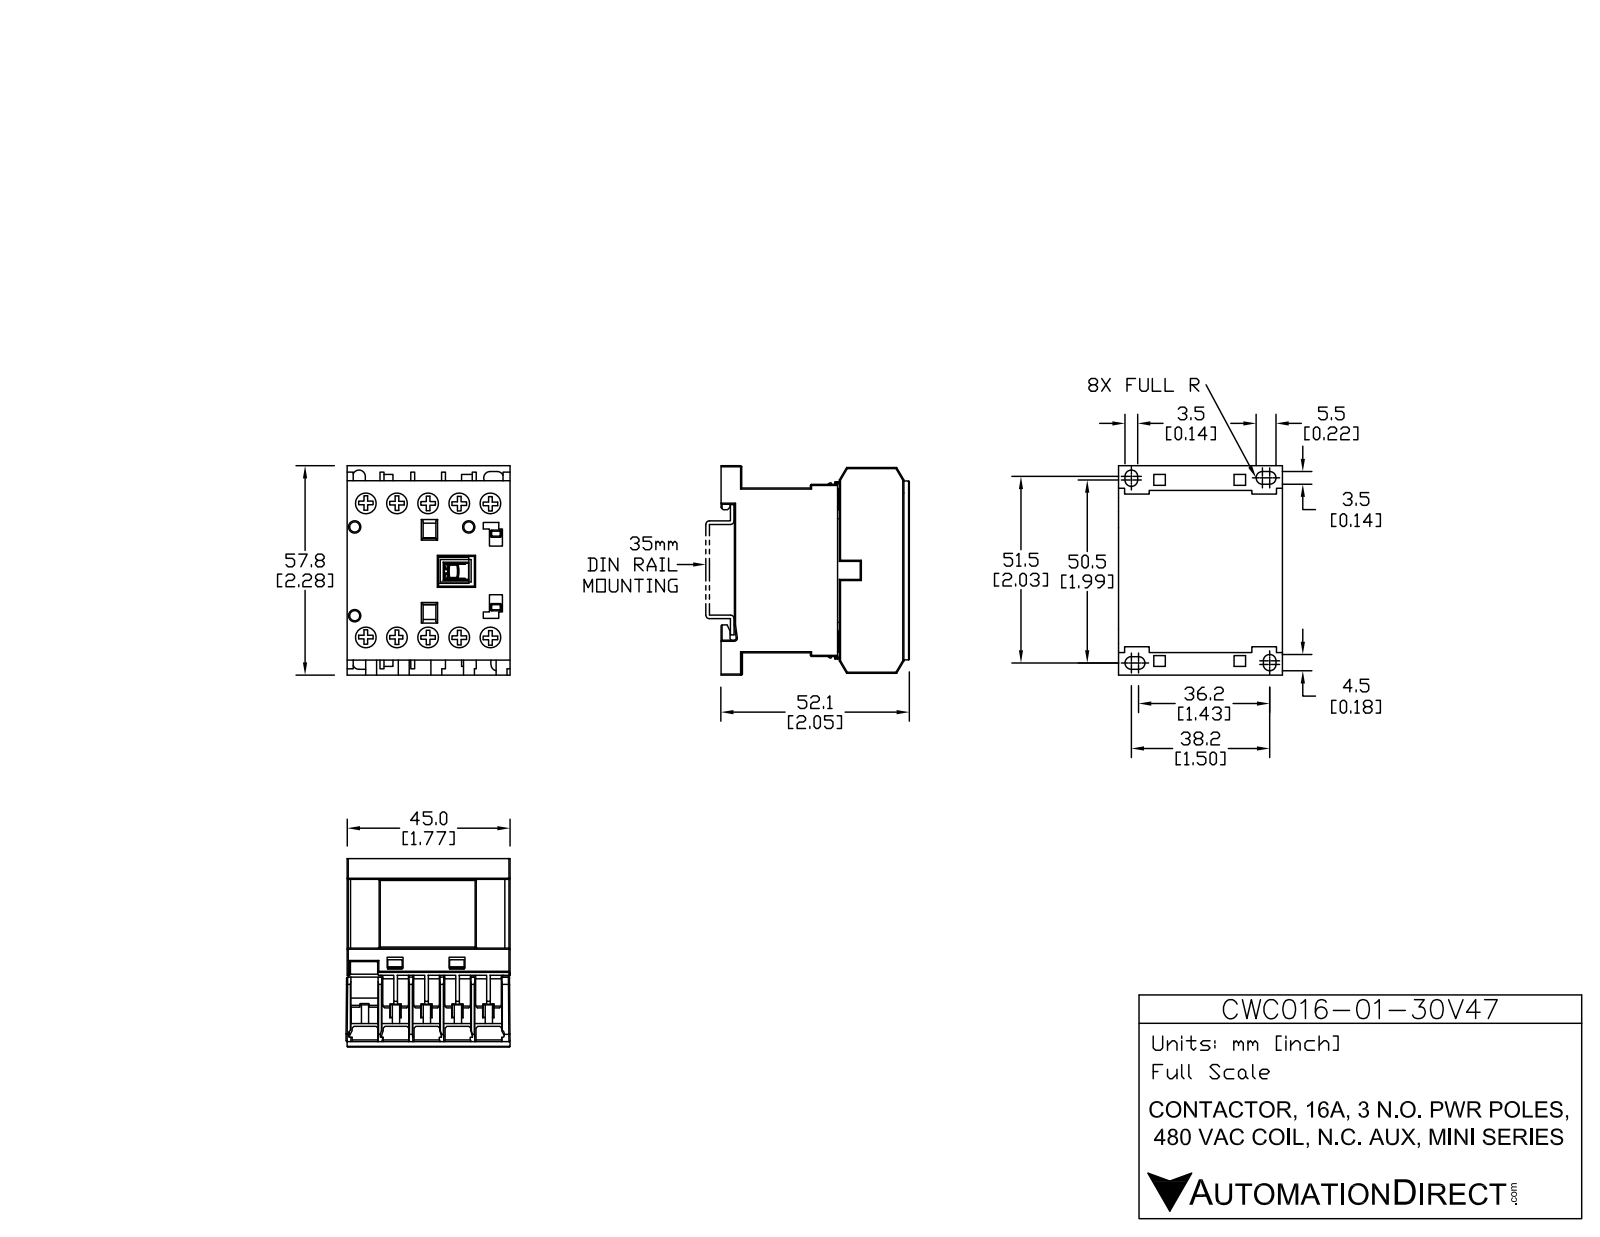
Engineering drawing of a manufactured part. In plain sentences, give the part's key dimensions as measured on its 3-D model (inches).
The part is named "CWC16-01-30V47". Its 3-D file was written by "SolidWorks 2013 (AUTOMOTIVE_DESIGN)". It is 15 solids with 535 faces: 445 planar, 90 cylindrical and 0 other. Overall it measures 2.285 by 2.052 by 1.801 inches. Its volume is 5.927 cubic inches and its surface area 47.18 square inches. Round holes: 10 of diameter 0.244, 3 of diameter 0.11. Round bosses or shafts: 10 of diameter 0.232. Partial cylindrical surfaces (rounded edges, fillets, slot ends): 20 of radius 0.012, 6 of radius 0.068, 2 of radius 0.068, 1 of radius 0.013, 1 of radius 0.017, 1 of radius 0.022. The main face-to-face distances are 0.325, 1.791, 0.049, 0.65, 0.374, 0.217, 0.699, 0.202, 0.419, 0.276. The hole center spacings are 0.337, 1.494, 0.673, 1.603, 1.455, 1.01, 1.771, 0.272.
